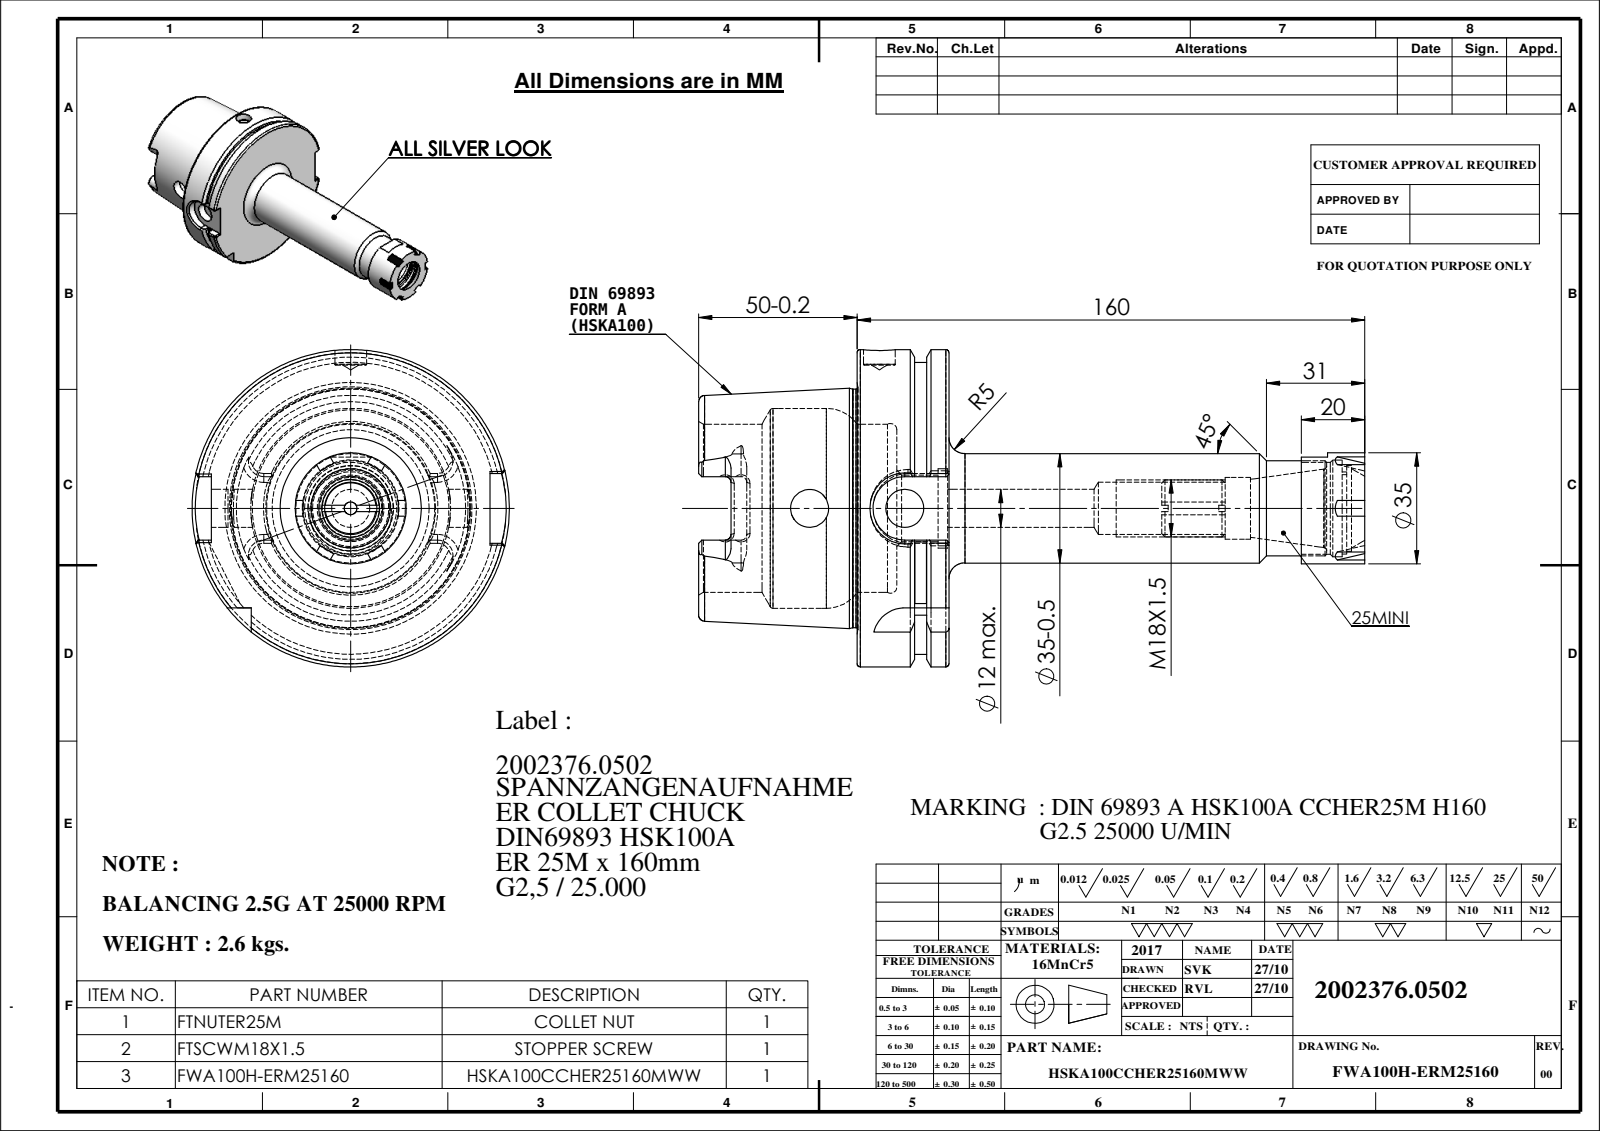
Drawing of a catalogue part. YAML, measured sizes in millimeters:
part_name: "FTSCWM18X150; FTNUTER25M; HSKA100CCHER25160MWW; 91100A-ERM25160"
step_written_by: "SolidWorks 2009 (CONFIG_CONTROL_DESIGN)"
units: millimeters
bodies: {solids: 3, faces: 248, planar: 96, cylindrical: 70, other: 82}
overall_size: [210, 100, 100]
volume: 347093
surface_area: 74956
round_holes:
  - {diameter: 12, count: 3}
  - {diameter: 4, count: 1}
  - {diameter: 10, count: 1}
  - {diameter: 16.5, count: 1}
  - {diameter: 19.5, count: 1}
  - {diameter: 21, count: 1}
  - {diameter: 25, count: 1}
  - {diameter: 25.8, count: 1}
  - {diameter: 27, count: 1}
  - {diameter: 29, count: 1}
  - {diameter: 30.5, count: 1}
  - {diameter: 53, count: 1}
round_bosses_or_shafts:
  - {diameter: 100, count: 1}
  - {diameter: 92, count: 1}
  - {diameter: 75.16, count: 1}
  - {diameter: 35, count: 1}
  - {diameter: 34.5, count: 1}
  - {diameter: 30, count: 1}
  - {diameter: 18, count: 1}
partial_cylinders:
  - {radius: 1.8, count: 6}
  - {radius: 4.88, count: 4}
  - {radius: 10, count: 2}
  - {radius: 11, count: 1}
  - {radius: 11.5, count: 1}
face_to_face_distances: [28.95, 12.5, 16.45, 50, 62.5, 78.95, 210, 160, 147.5, 131.05]
hole_center_spacings: [1.5, 30]
